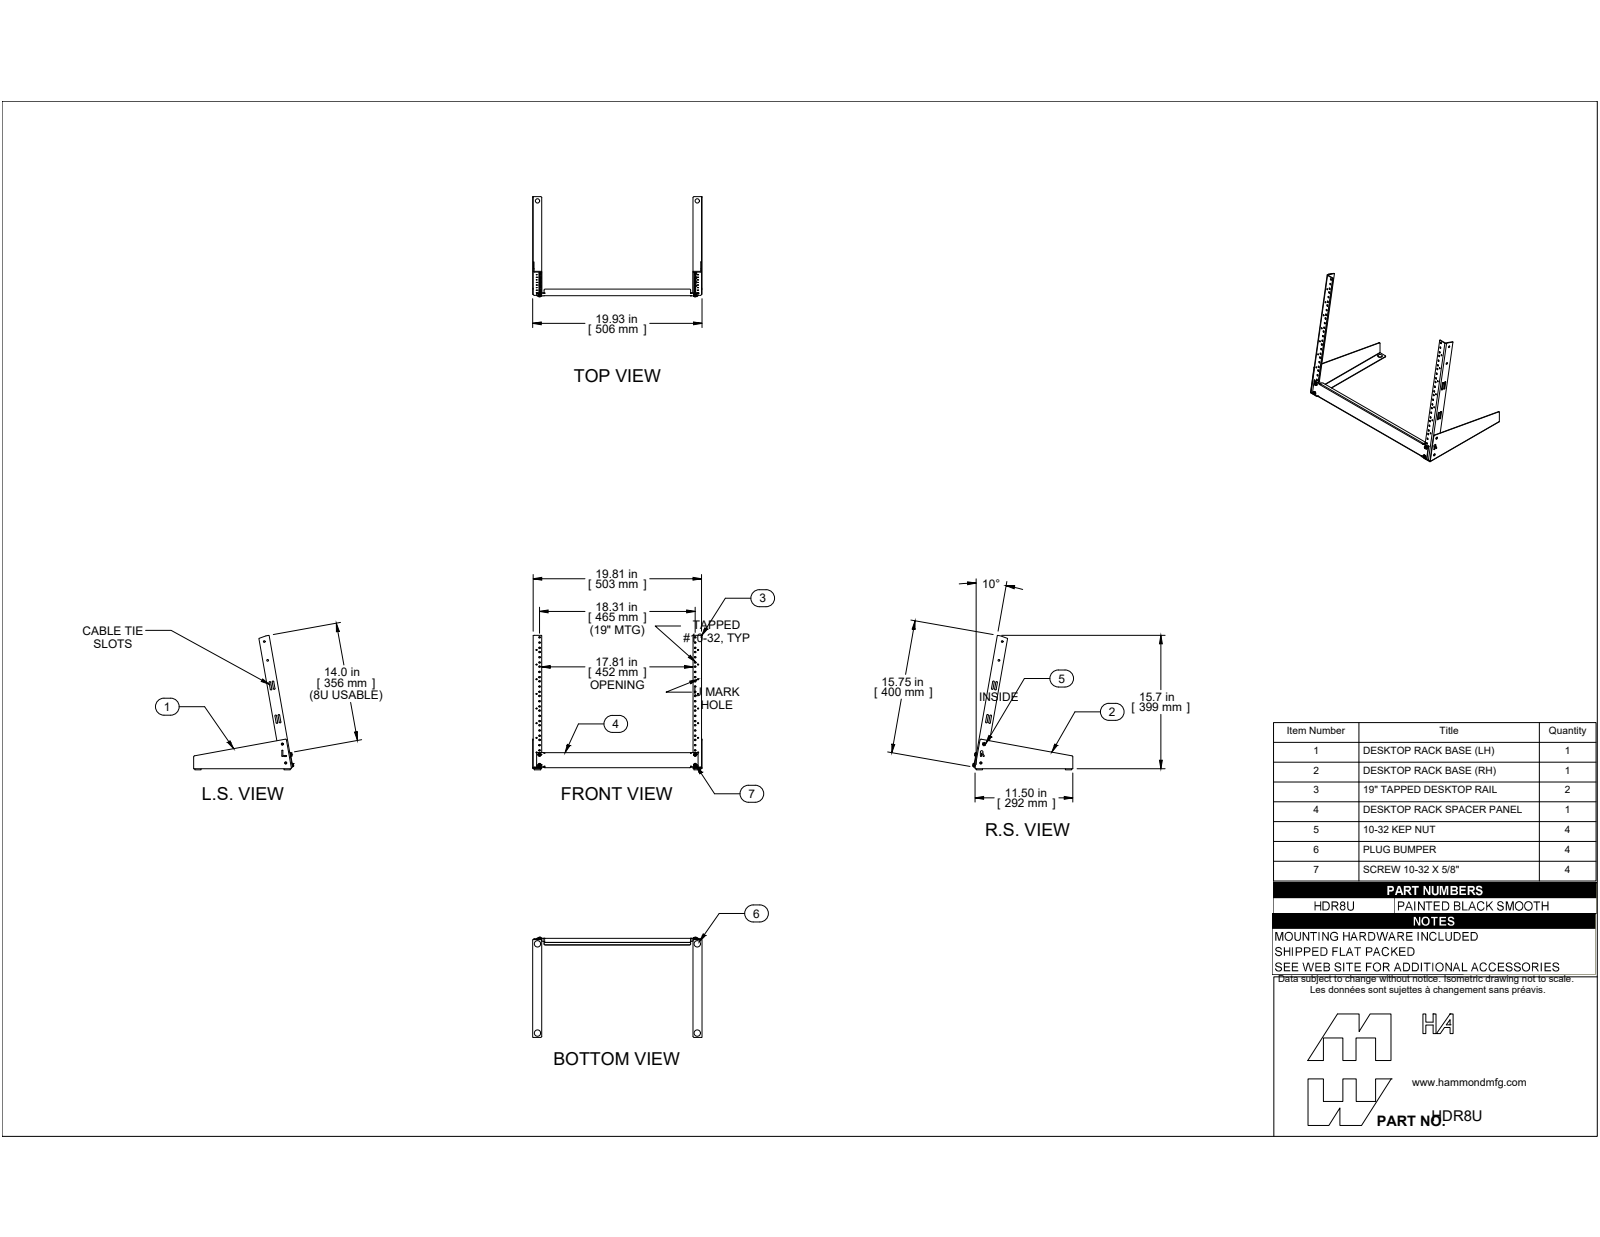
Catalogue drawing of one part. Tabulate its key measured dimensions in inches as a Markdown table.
| quantity | value |
| --- | --- |
| part name | HDR8UBK |
| STEP written by | SolidWorks 2019 (CONFIG_CONTROL_DESIGN) |
| units | inches |
| bodies | 21 solids, 400 faces (216 planar, 176 cylindrical, 8 other) |
| overall size | 19.926 × 15.82 × 11.773 |
| volume | 13.65 in³ |
| surface area | 407 in² |
| round holes (diameter × count) | 0.177 × 54, 0.125 × 16, 0.198 × 4, 0.206 × 4, 0.5 × 4, 0.156 × 2, 0.189 × 2 |
| round bosses / shafts (diameter × count) | 0.368 × 8, 0.75 × 4, 0.189 × 4, 0.256 × 2, 0.19 × 2 |
| partial cylindrical surfaces (radius × count) | 0.125 × 15, 0.094 × 8, 0.029 × 4, 0.063 × 4, 0.086 × 4, 0.062 × 3, 0.048 × 2, 0.143 × 2 |
| main face-to-face distances | 0.057, 19.87, 19.813, 0.152, 0.095, 0.095, 19.927, 0.152, 19.718, 19.775 |
| hole center spacings | 1.75, 1.125, 7, 0.625, 5.25, 5.875, 2.875, 3.5 |
